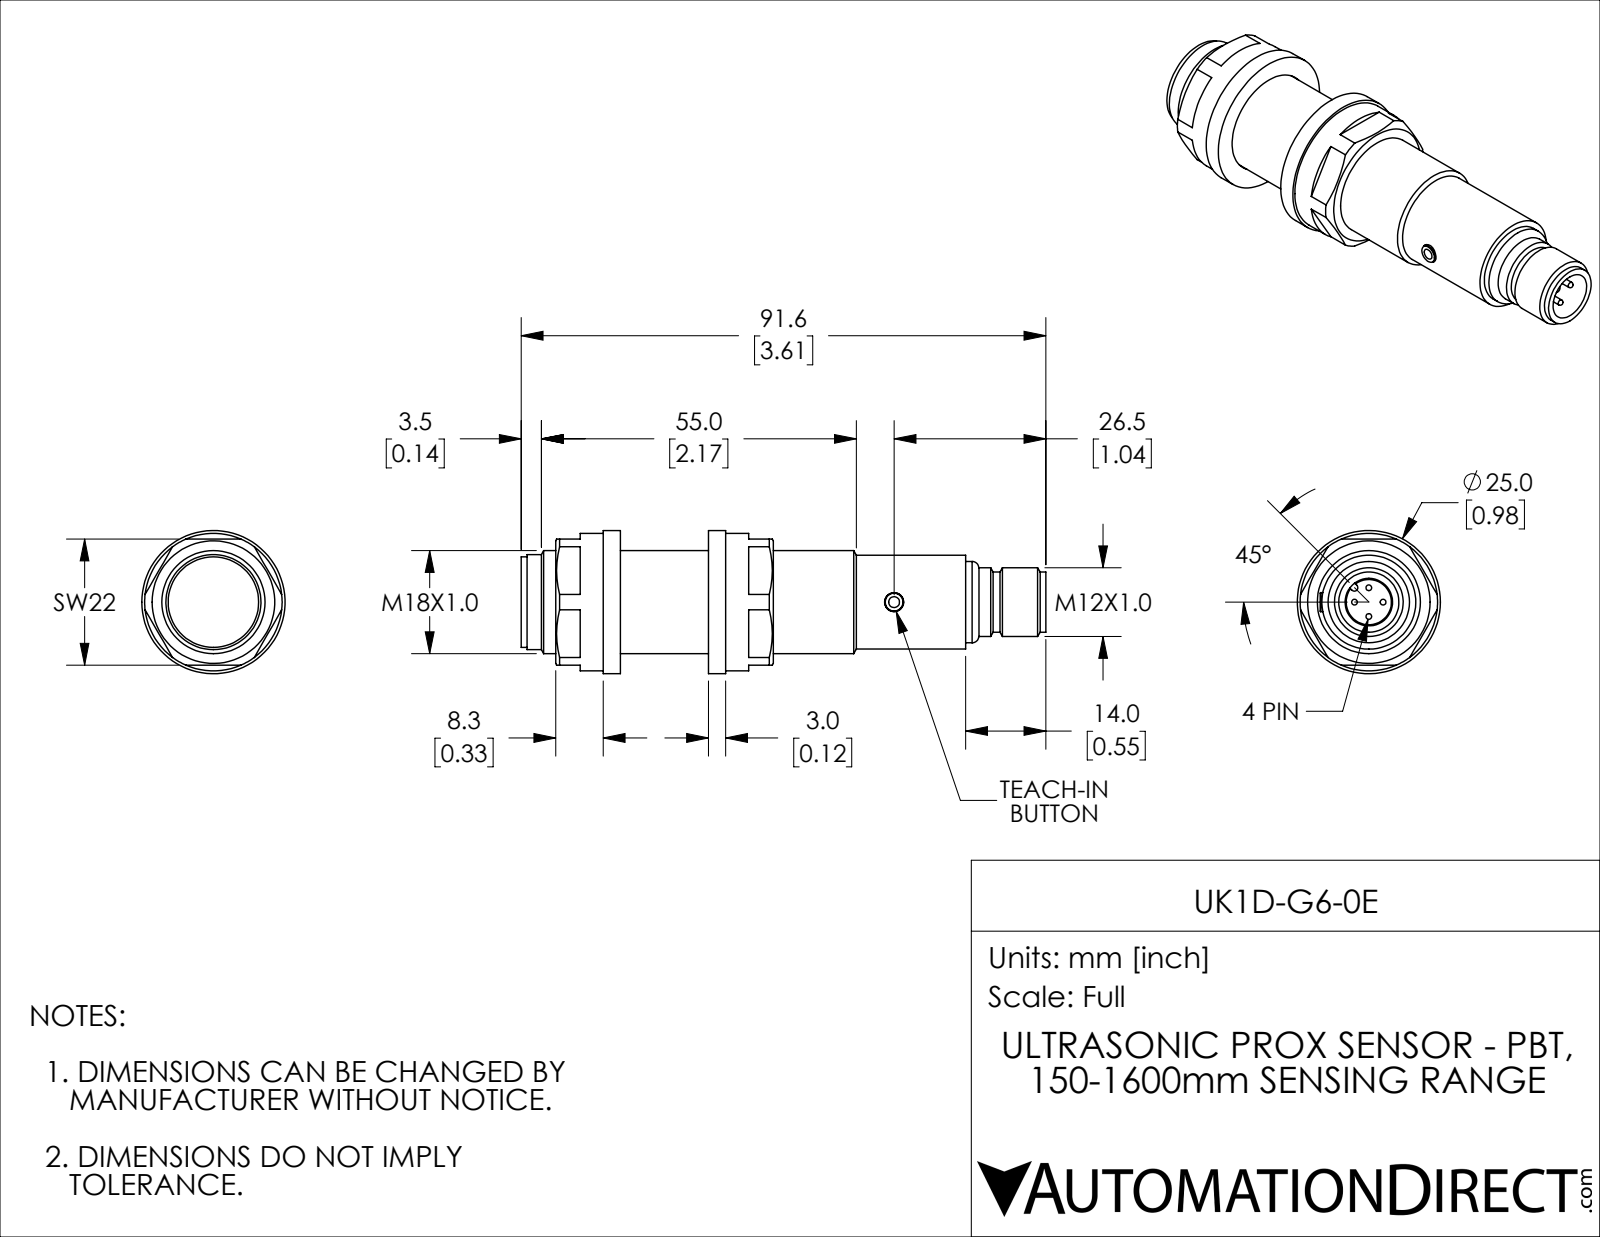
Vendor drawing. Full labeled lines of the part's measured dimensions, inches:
Part name (STEP PRODUCT): UK1D-G6-0E
STEP written by: SolidWorks 2018 (AUTOMOTIVE_DESIGN)
Units: inches
Bodies: 6 solids, 123 faces (43 planar, 49 cylindrical, 31 other)
Overall size (bounding box): 3.606 × 0.984 × 0.984
Volume: 1.477 in³ · Surface area: 16.01 in²
Round holes (diameter × count): ⌀0.13 ×1, ⌀0.327 ×1, ⌀0.709 ×1, ⌀0.717 ×1
Round bosses / shafts (diameter × count): ⌀0.039 ×4, ⌀0.984 ×1, ⌀0.945 ×1, ⌀0.654 ×1, ⌀0.646 ×1, ⌀0.622 ×1, ⌀0.559 ×1, ⌀0.472 ×1
Partial cylindrical surfaces — rounded edges, fillets, slot ends (radius × count): R0.024 ×1
Main face-to-face distances: 0.118, 0.724, 0.843, 0.606, 0.866, 0.327, 0.445, 1.051, 1.169, 0.563
